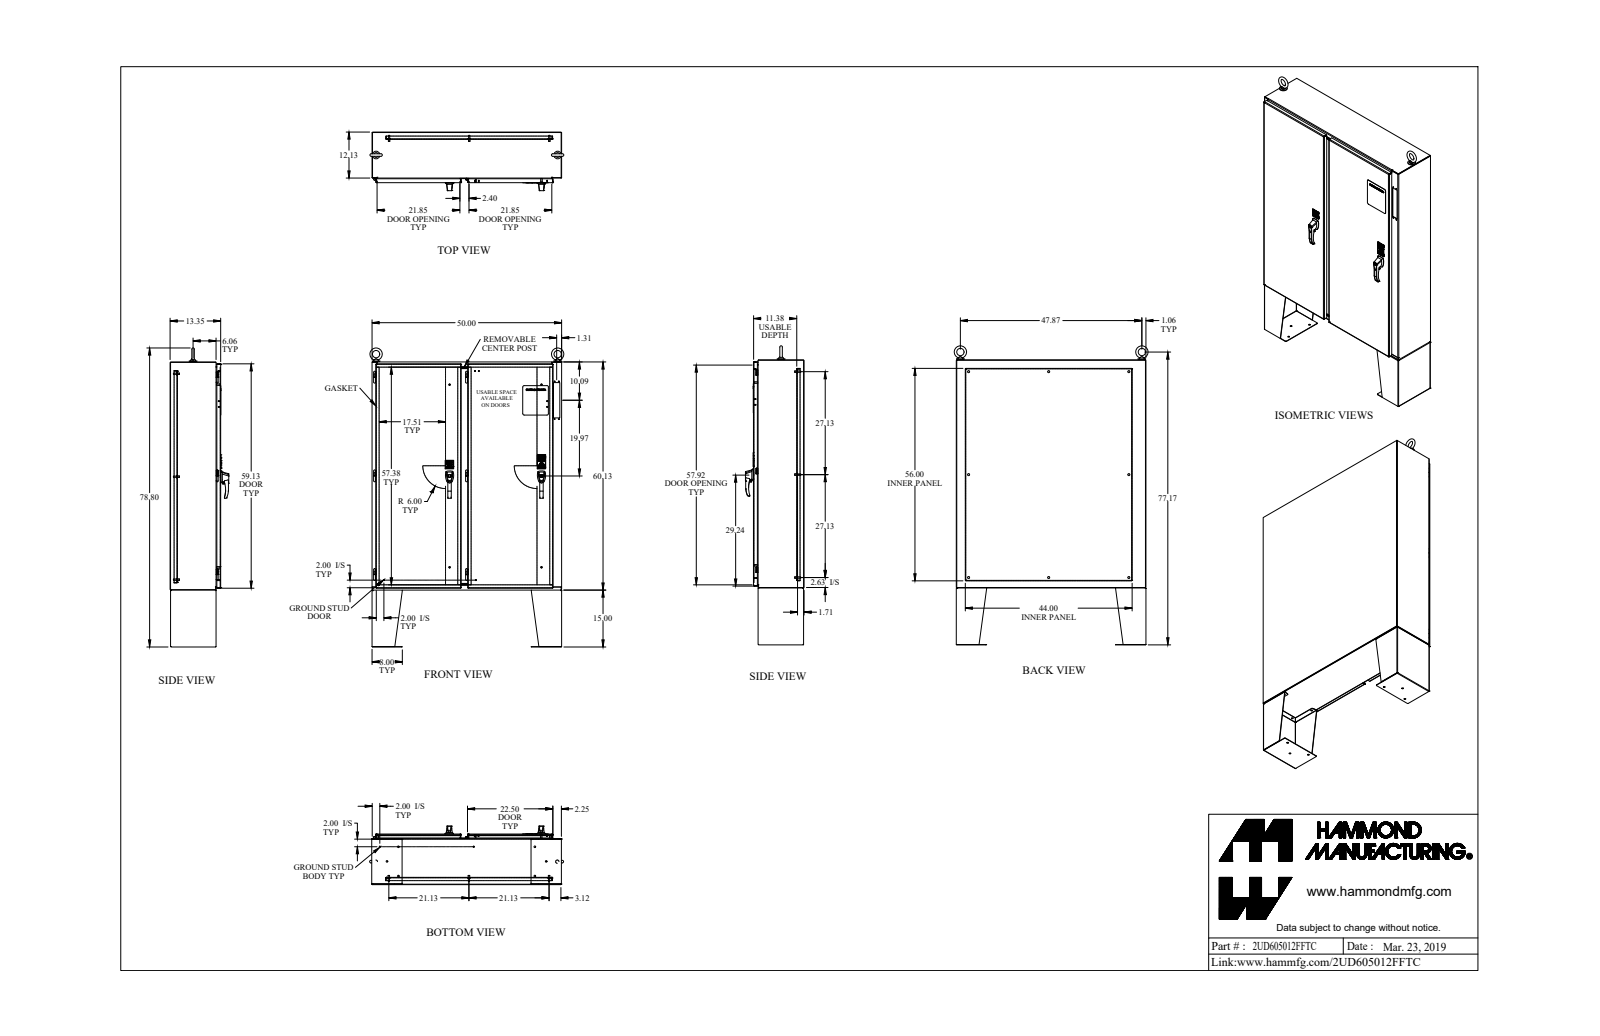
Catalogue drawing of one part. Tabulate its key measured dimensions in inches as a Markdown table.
| quantity | value |
| --- | --- |
| part name | 2UD605012FFTC |
| STEP written by | SolidWorks 2018 (AUTOMOTIVE_DESIGN) |
| units | inches |
| bodies | 217 solids, 3615 faces (2042 planar, 1041 cylindrical, 532 other) |
| overall size | 78.799 × 51.122 × 15.466 |
| volume | 1 887 in³ |
| surface area | 30 752 in² |
| round holes (diameter × count) | 0.437 × 14, 0.281 × 11, 0.307 × 11, 0.196 × 10, 0.25 × 10, 0.35 × 8, 0.563 × 8, 0.257 × 6, 0.313 × 6, 0.445 × 5, 0.28 × 4, 0.282 × 4 |
| round bosses / shafts (diameter × count) | 0.25 × 21, 1 × 14, 0.65 × 9, 0.375 × 9, 0.33 × 9, 0.281 × 8, 0.75 × 6, 0.53 × 6 |
| partial cylindrical surfaces (radius × count) | 0.06 × 63, 0.125 × 62, 0.185 × 42, 0.5 × 38, 0.017 × 32, 0.03 × 28, 0.01 × 20, 0.048 × 20 |
| main face-to-face distances | 0.125, 0.125, 1.812, 13.1, 13.225, 13.226, 13.35, 11.289, 11.414, 1.937 |
| hole center spacings | 24.25, 58.452, 4.888, 5.076, 6.126, 9.964, 27.554, 39.192 |
